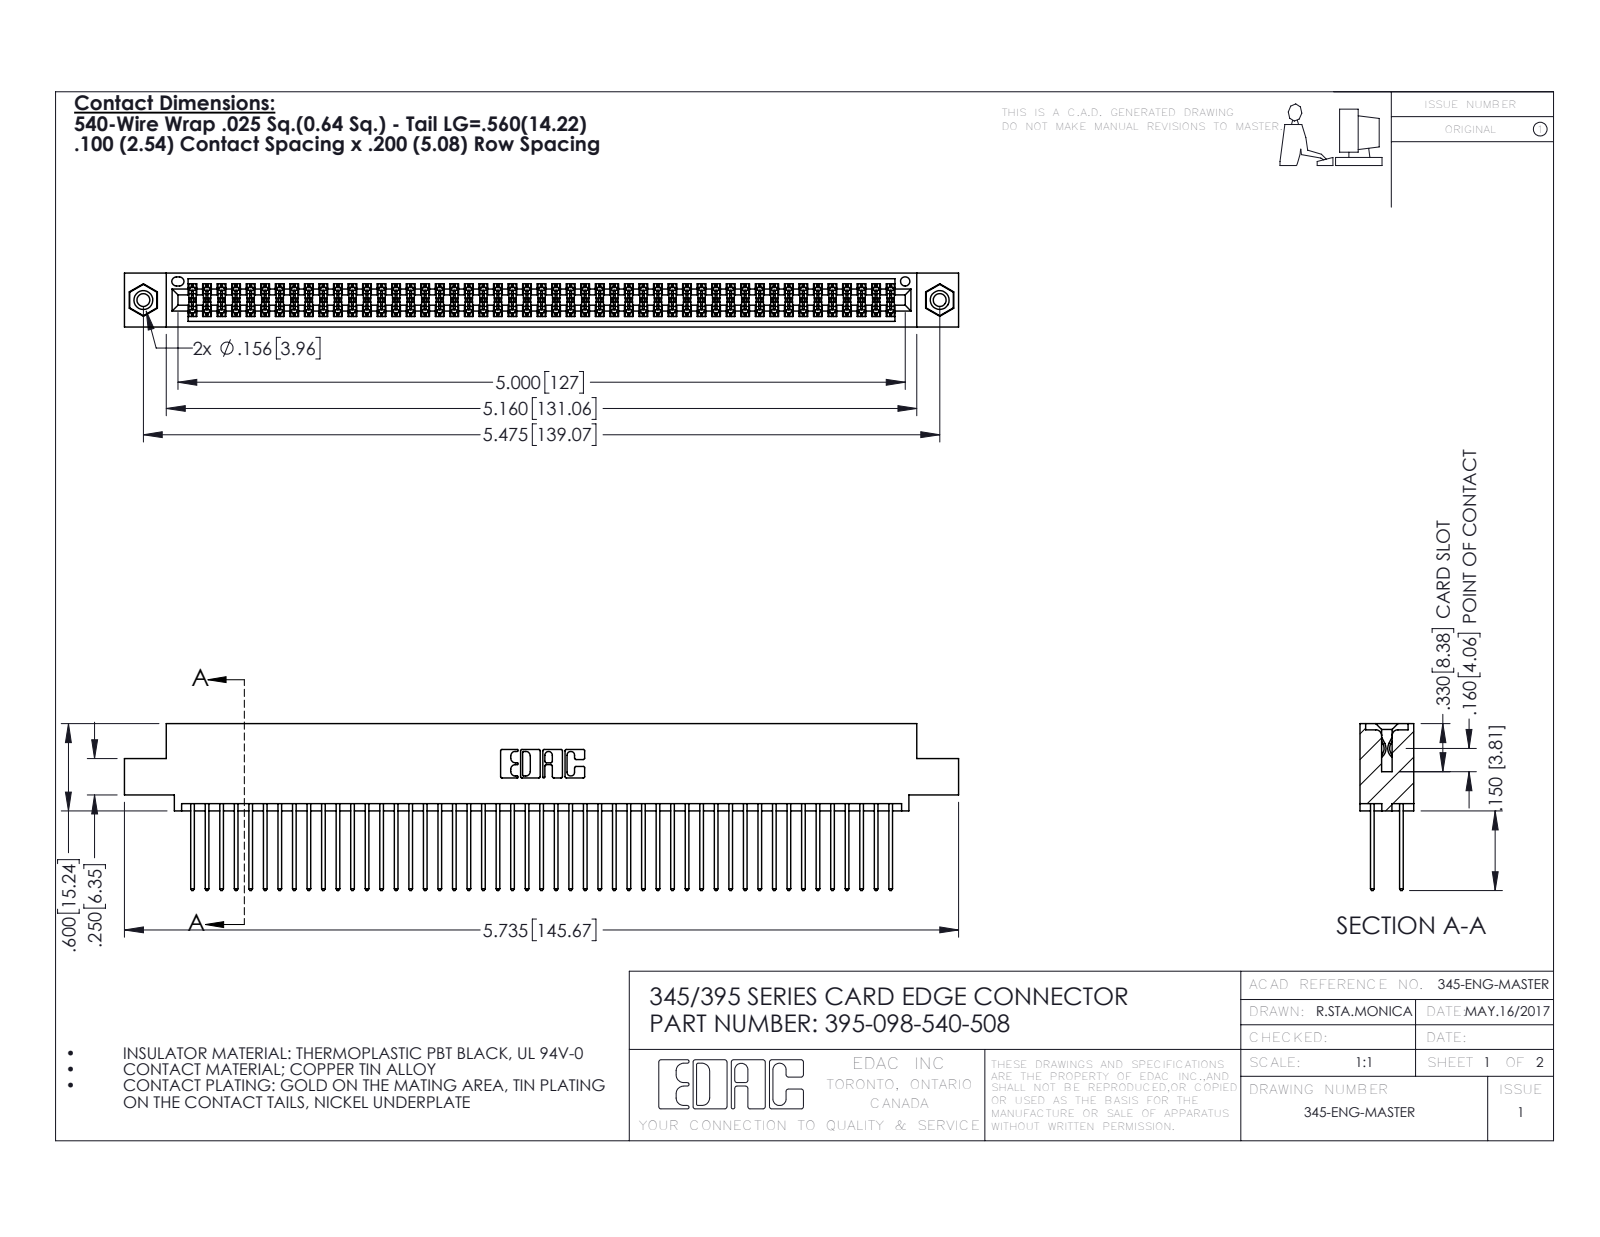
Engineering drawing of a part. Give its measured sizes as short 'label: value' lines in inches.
name: 345 Part_0.110 Offset - 0.156 Dia-TI; 345-250-001_345-250-003-102; 395-098-540-508; 345-292-001_345-293-140
written by: SolidWorks 2016 (CONFIG_CONTROL_DESIGN)
unit: in
bodies: 101 solids, 5090 faces (3350 planar, 1724 cylindrical, 16 other)
size: 5.735 × 1.147 × 0.37
volume: 0.885 in³; area: 36.28 in²
holes: 2× ⌀0.089, 2× ⌀0.125, 2× ⌀0.156, 1× ⌀0.064
bosses: 2× ⌀0.155
rounds: 147× R0.006, 98× R0.01, 22× R0.01, 6× R0.007, 6× R0.031, 3× R0.026, 2× R0.014, 2× R0.019
face distances: 0.072, 0.298, 0.2, 0.098, 0.272, 0.025, 0.37, 0.225, 0.175, 0.149
hole spacings: 0.27, 5.239, 5.475
